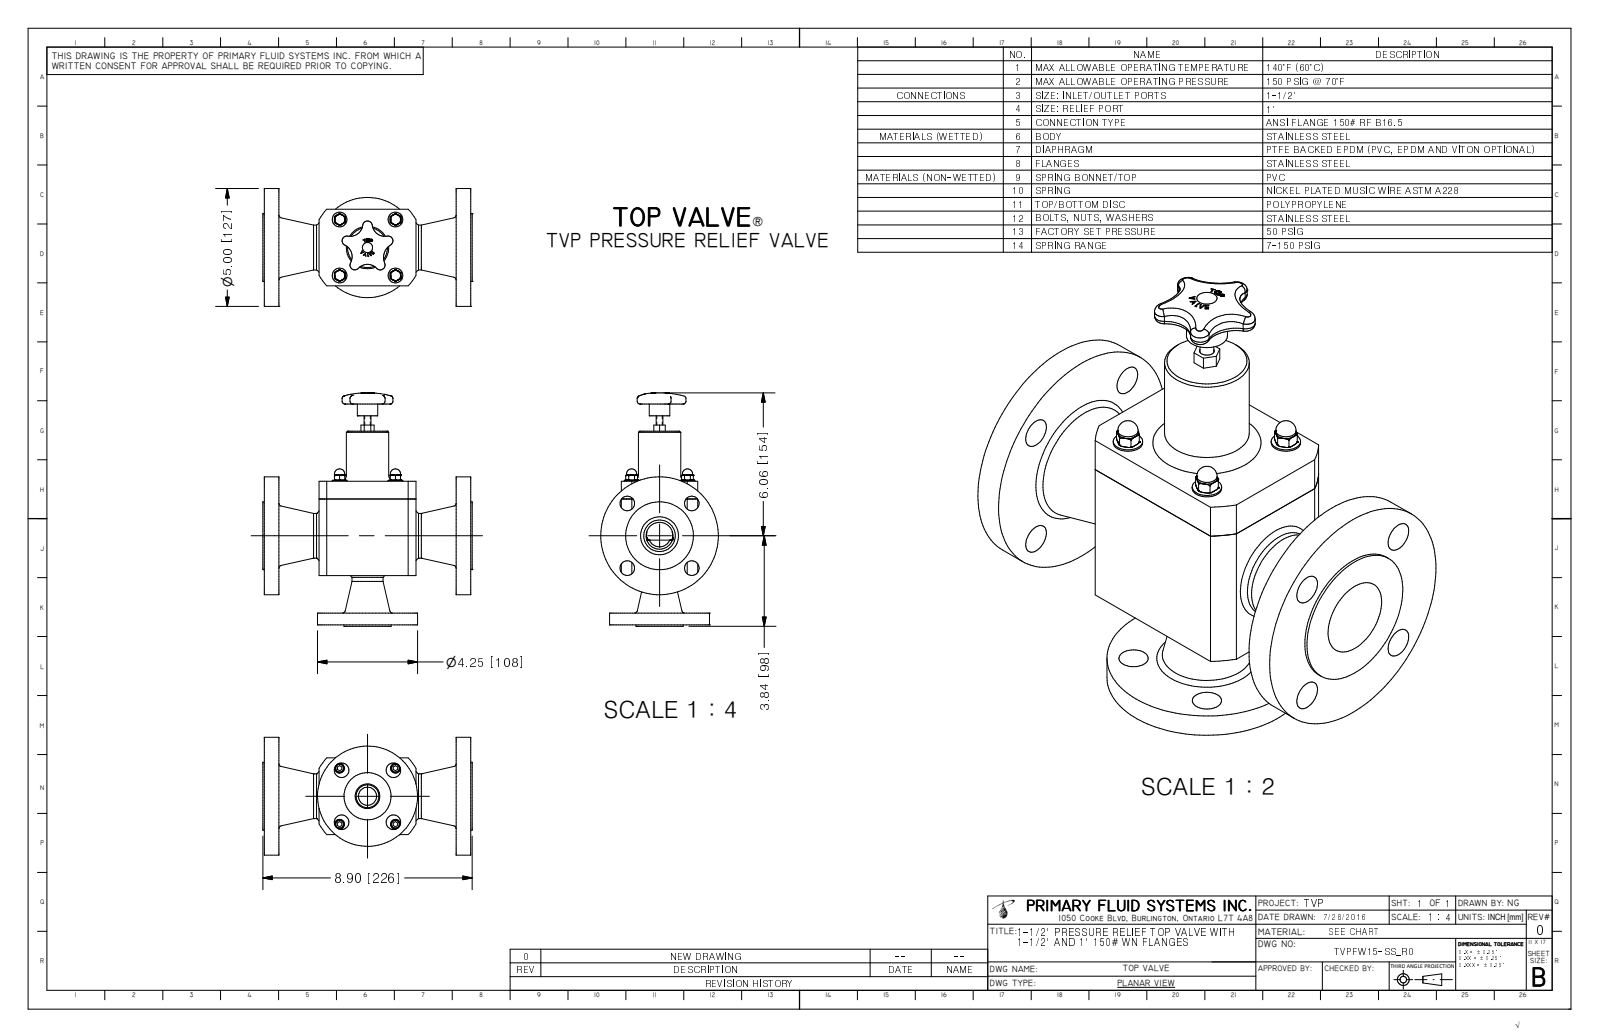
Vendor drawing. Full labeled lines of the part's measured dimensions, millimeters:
Part name (STEP PRODUCT): TVPFW15-SS_R0
STEP written by: Autodesk Inventor 2009 (AUTOMOTIVE_DESIGN)
Units: millimetres
Bodies: 1 solid, 376 faces (154 planar, 67 cylindrical, 155 other)
Overall size (bounding box): 251.5 × 225.9 × 127
Volume: 1 501 000 mm³ · Surface area: 192 600 mm²
Round holes (diameter × count): ⌀15.7 ×8, ⌀4.4 ×4, ⌀26.6 ×1, ⌀40.9 ×1
Round bosses / shafts (diameter × count): ⌀15.9 ×4, ⌀11 ×4, ⌀9.5 ×4, ⌀127 ×1, ⌀108 ×1, ⌀73.2 ×1, ⌀50.8 ×1, ⌀48.3 ×1
Partial cylindrical surfaces — rounded edges, fillets, slot ends (radius × count): R2.2 ×5, R5.2 ×5, R13.6 ×4, R16.7 ×4, R15.9 ×1, R18.9 ×1, R60.3 ×1
Main face-to-face distances: 15.7, 207, 82.6, 191.3, 222.8, 59, 163.8, 43.2, 148, 53.1
Hole centre spacings: 39.6, 49.3, 56, 58.2, 69.7, 3, 3, 42.6
